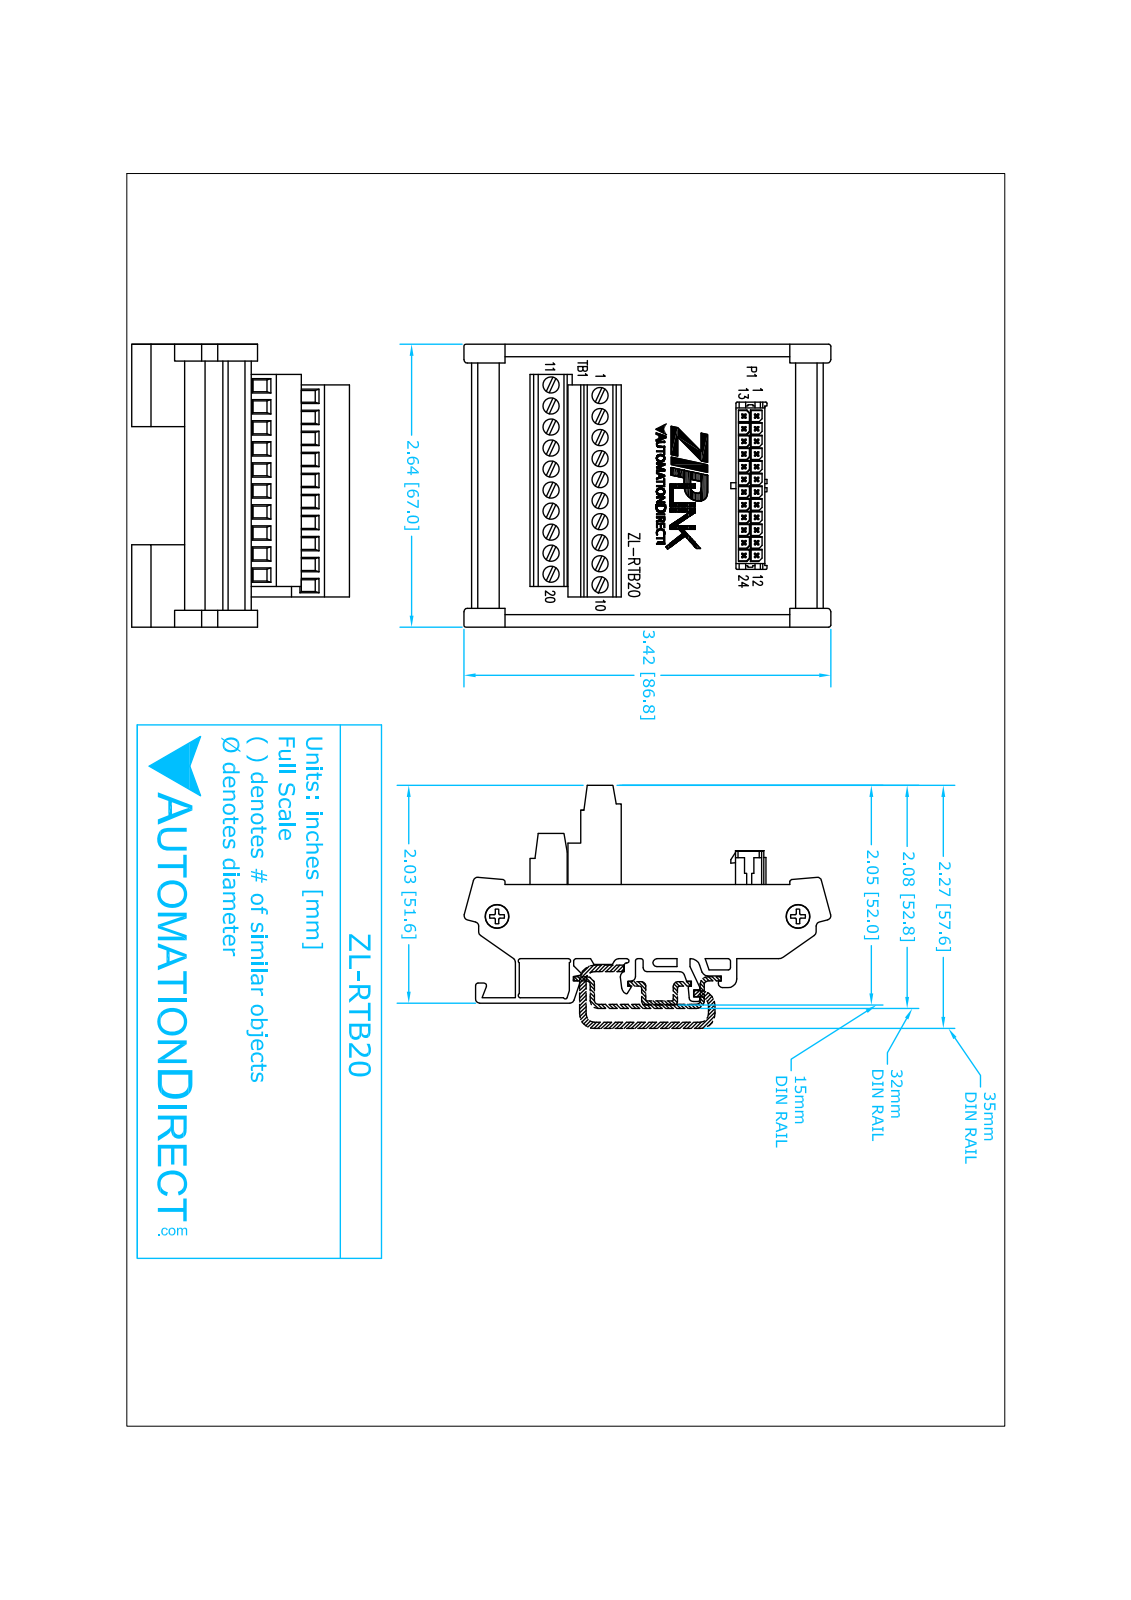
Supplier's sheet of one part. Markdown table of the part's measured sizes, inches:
| quantity | value |
| --- | --- |
| part name | ZL-RTB20 |
| STEP written by | SolidWorks 2014 (AUTOMOTIVE_DESIGN) |
| units | inches |
| bodies | 1 solid, 869 faces (704 planar, 157 cylindrical, 8 other) |
| overall size | 3.42 × 2.696 × 2.03 |
| volume | 6.749 in³ |
| surface area | 50.08 in² |
| round holes (diameter × count) | 0.15 × 20, 0.225 × 2 |
| round bosses / shafts (diameter × count) | 0.205 × 2 |
| partial cylindrical surfaces (radius × count) | 0.015 × 41, 0.03 × 10 |
| main face-to-face distances | 0.628, 2.64, 0.03, 0.658, 0.452, 1.08, 1.11, 0.1, 1.85, 0.5 |
| hole center spacings | 0.196, 0.392, 0.462, 0.461, 0.537, 0.539, 0.588, 0.784 |
